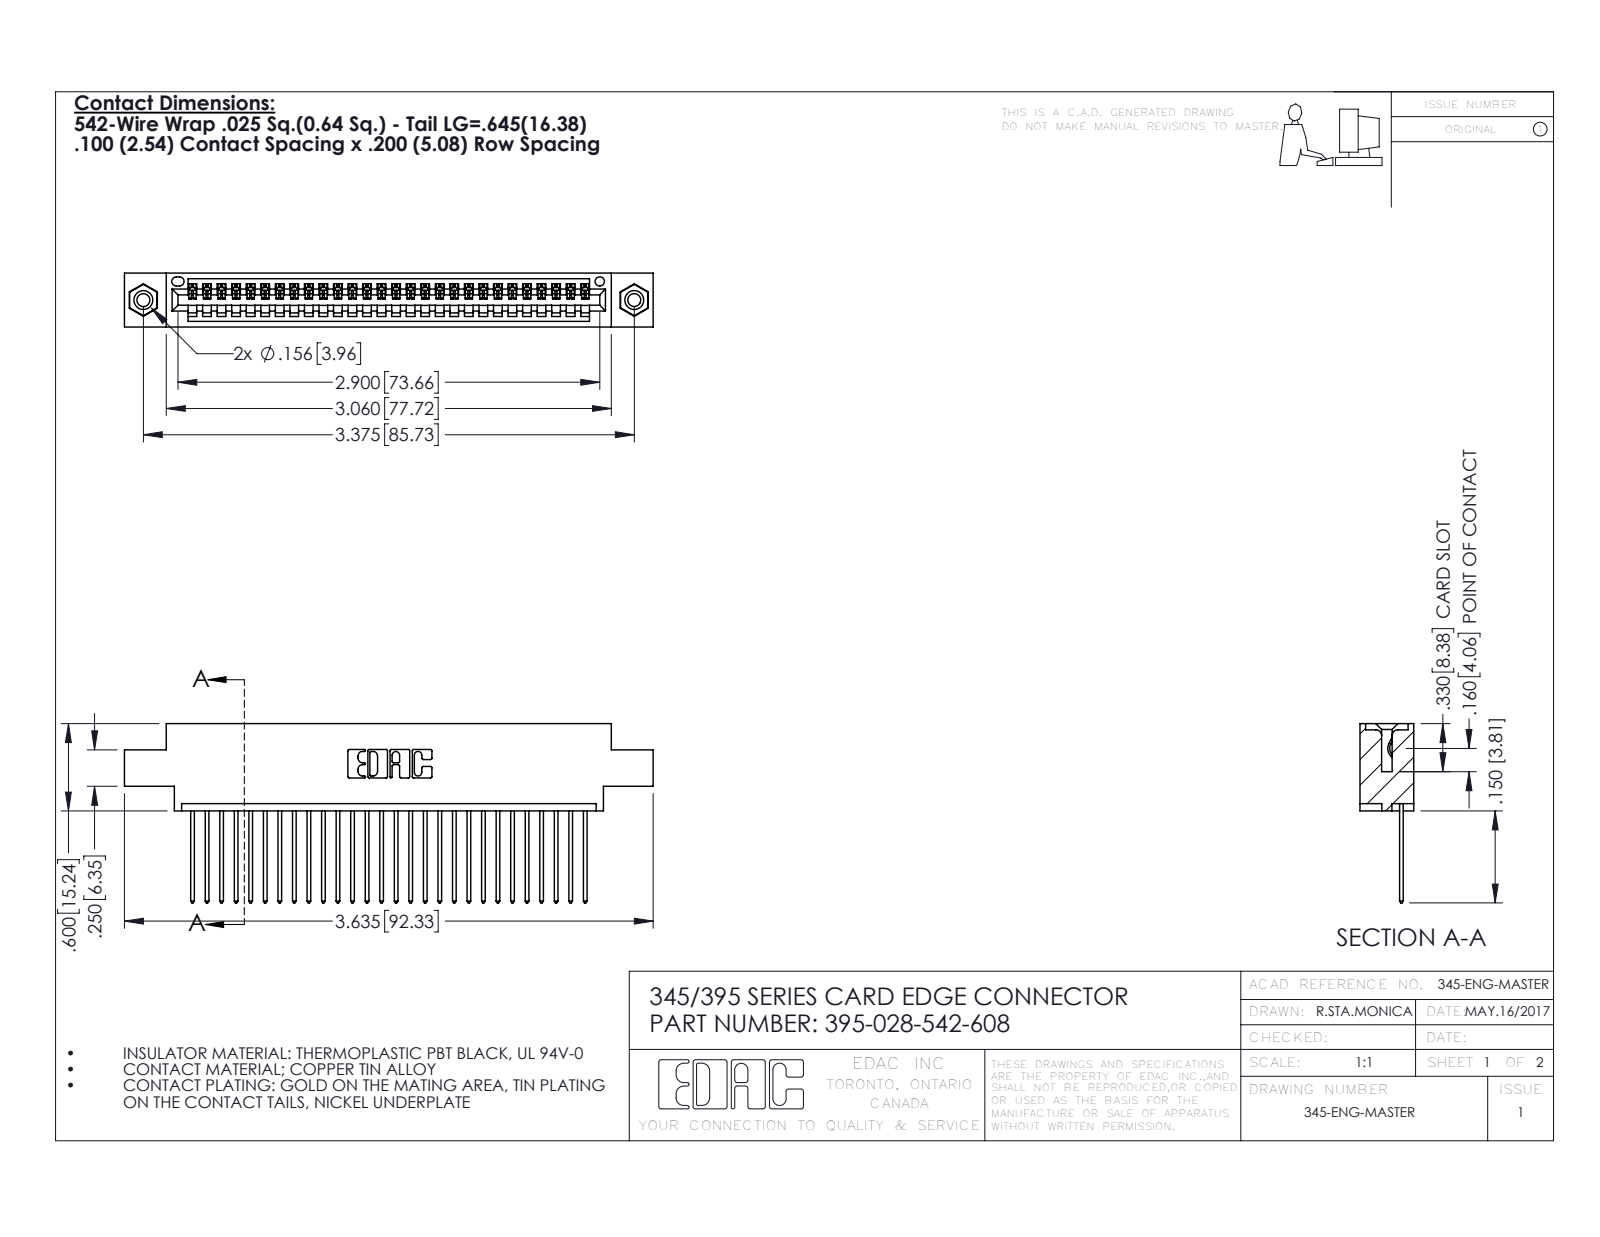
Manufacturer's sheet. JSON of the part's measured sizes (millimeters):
{"part_name": "345-250-001_345-250-003-102; 345-292-001_345-293-142; 395-028-542-608; 345 Part_0.170 Offset - 0.156 Dia-TI", "step_written_by": "SolidWorks 2016 (CONFIG_CONTROL_DESIGN)", "units": "millimeters", "bodies": {"solids": 31, "faces": 1814, "planar": 1236, "cylindrical": 562, "other": 16}, "overall_size": [92.3, 31.3, 9.4], "volume_mm3": 8600, "surface_area_mm2": 11770, "round_holes": [[2.3, 2], [3.2, 2], [4, 2], [1.6, 1]], "round_bosses_or_shafts": [[3.9, 2]], "partial_cylinders_radius": [[0.2, 56], [0.3, 56], [0.3, 22], [0.2, 6], [0.8, 6], [0.7, 3], [0.8, 2], [1, 2]], "face_to_face_distances": [1.8, 7.6, 9.4, 2.5, 6.9, 0.6, 5.1, 5.7, 4.4, 3.8], "hole_center_spacings": [6.9, 79.8, 85.7]}
